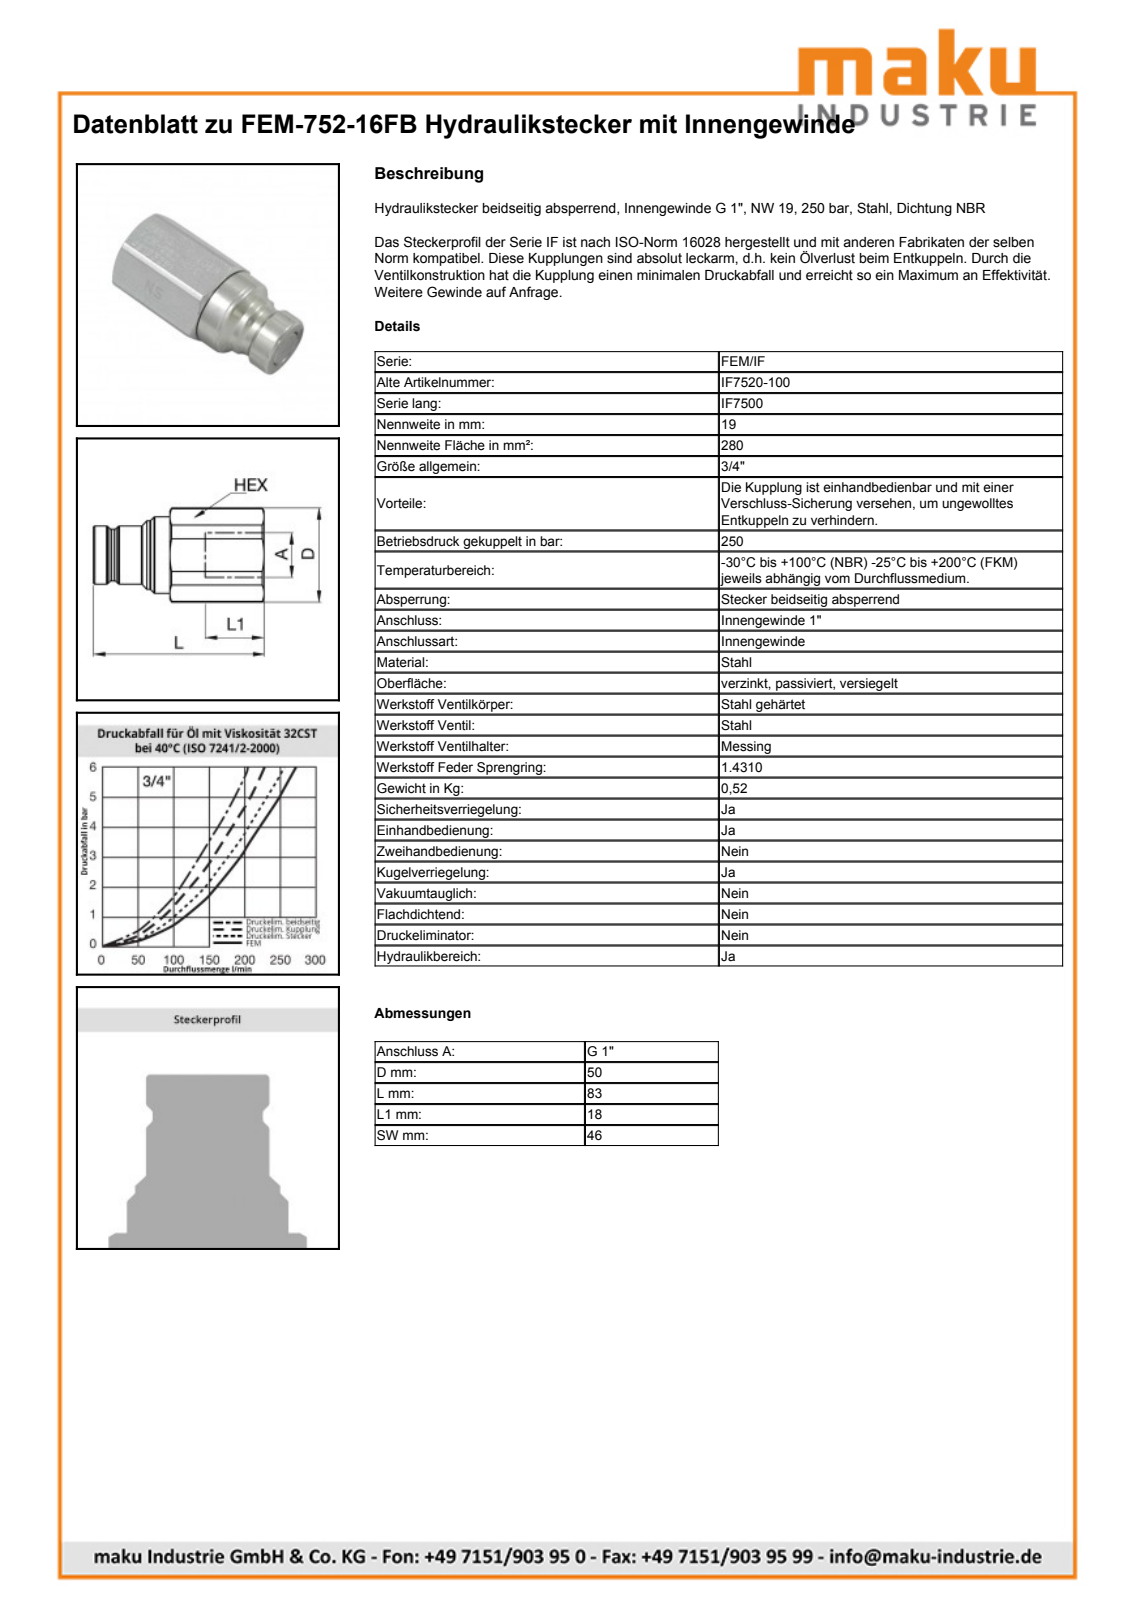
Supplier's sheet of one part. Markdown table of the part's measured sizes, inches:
| quantity | value |
| --- | --- |
| part name | FEM-752-16FB |
| STEP written by | SolidWorks 2009 (AUTOMOTIVE_DESIGN) |
| units | inches |
| bodies | 1 solid, 83 faces (13 planar, 24 cylindrical, 46 other) |
| overall size | 3.252 × 1.969 × 1.811 |
| volume | 5.666 in³ |
| surface area | 25.16 in² |
| round holes (diameter × count) | 0.815 × 1, 0.925 × 1, 1.193 × 1, 1.661 × 1 |
| round bosses / shafts (diameter × count) | 1.654 × 1, 1.498 × 1, 1.179 × 1, 1.059 × 1 |
| partial cylindrical surfaces (radius × count) | 0.984 × 1 |
| main face-to-face distances | 1.811, 0.959, 2.29, 3.249, 2.293, 3.252, 1.638, 1.635, 0.655, 1.614 |
